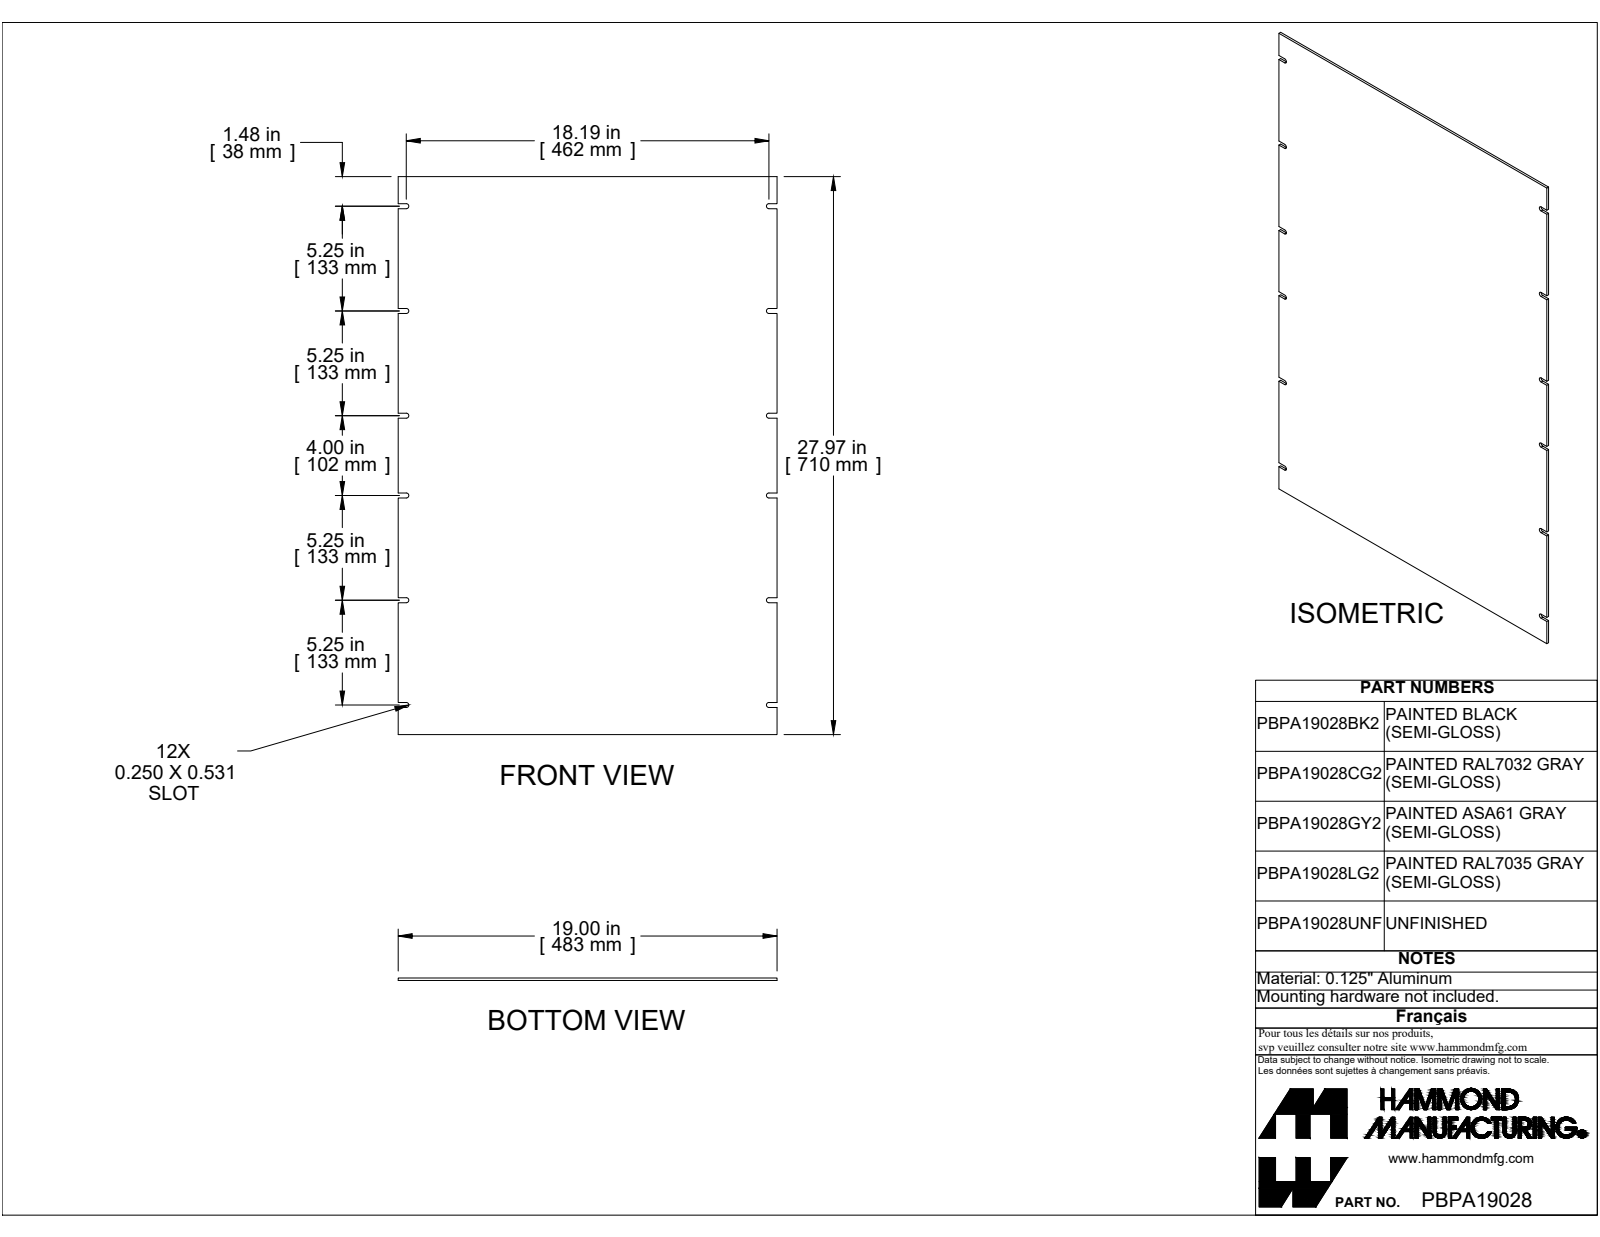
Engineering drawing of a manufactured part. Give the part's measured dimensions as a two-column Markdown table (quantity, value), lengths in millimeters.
| quantity | value |
| --- | --- |
| part name | PBPA19028LG2 |
| STEP written by | SolidWorks 2019 (CONFIG_CONTROL_DESIGN) |
| units | millimeters |
| bodies | 1 solid, 54 faces (42 planar, 12 cylindrical, 0 other) |
| overall size | 710.4 × 482.6 × 3.2 |
| volume | 1 085 000 mm³ |
| surface area | 692 300 mm² |
| partial cylindrical surfaces (radius × count) | 3.2 × 12 |
| main face-to-face distances | 3.2, 482.6, 710.4, 6.4, 133.4, 266.7, 368.3, 501.7, 133.4, 235 |
